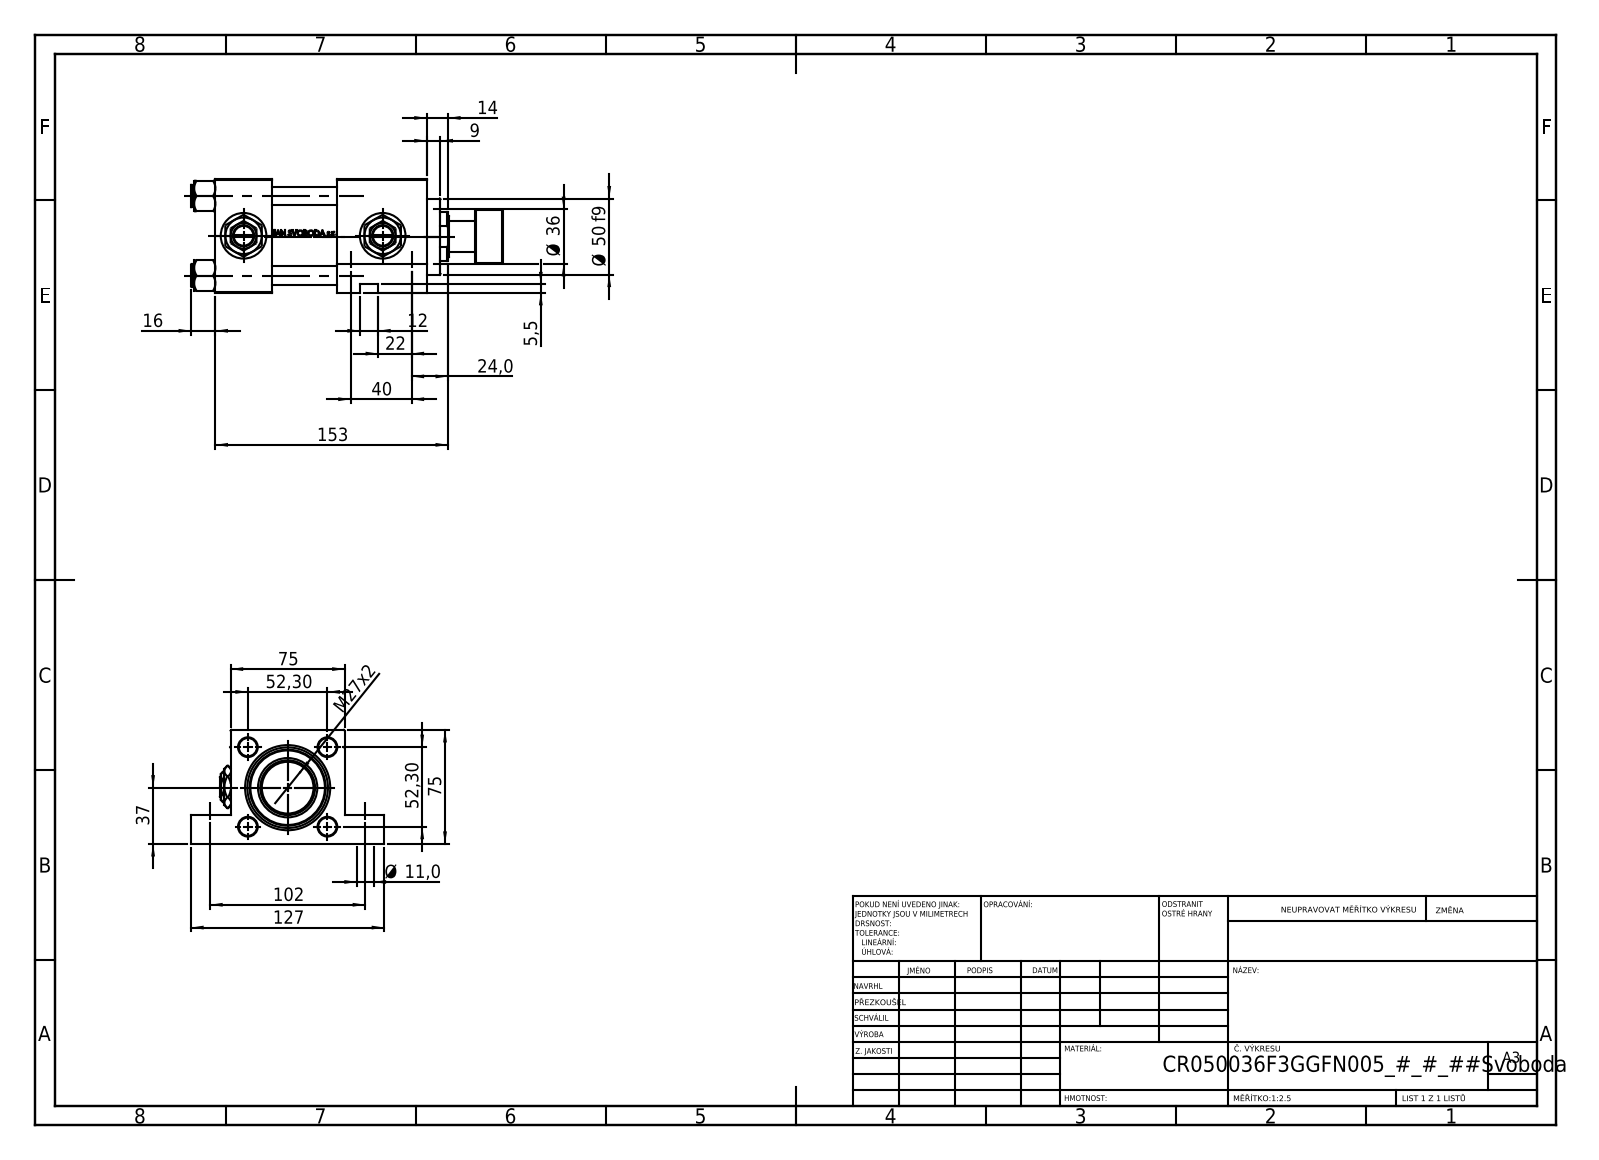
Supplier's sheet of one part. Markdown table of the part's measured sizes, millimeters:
| quantity | value |
| --- | --- |
| part name | V215CR_F_Body; V215CR_VCP_F; NUT_M5_F; V215_VC_A (+3 more) |
| STEP written by | SolidWorks 2019 (CONFIG_CONTROL_DESIGN) |
| units | millimeters |
| bodies | 14 solids, 1196 faces (488 planar, 136 cylindrical, 572 other) |
| overall size | 205 × 127 × 75 |
| volume | 702 406 mm³ |
| surface area | 163 863 mm² |
| round holes (diameter × count) | 12 × 4, 20.96 × 4, 30 × 4, 7 × 3, 11 × 2, 11 × 2, 25.5 × 1, 36 × 1, 39 × 1, 41 × 1, 53 × 1 |
| round bosses / shafts (diameter × count) | 15 × 4, 56 × 1, 50 × 1, 35 × 1, 21 × 1 |
| main face-to-face distances | 75, 37, 43, 80, 59, 139, 102, 56, 19, 26 |
| hole center spacings | 52.3, 36.63, 37.34, 40, 51.62, 60.21, 73.96, 87.01 |
